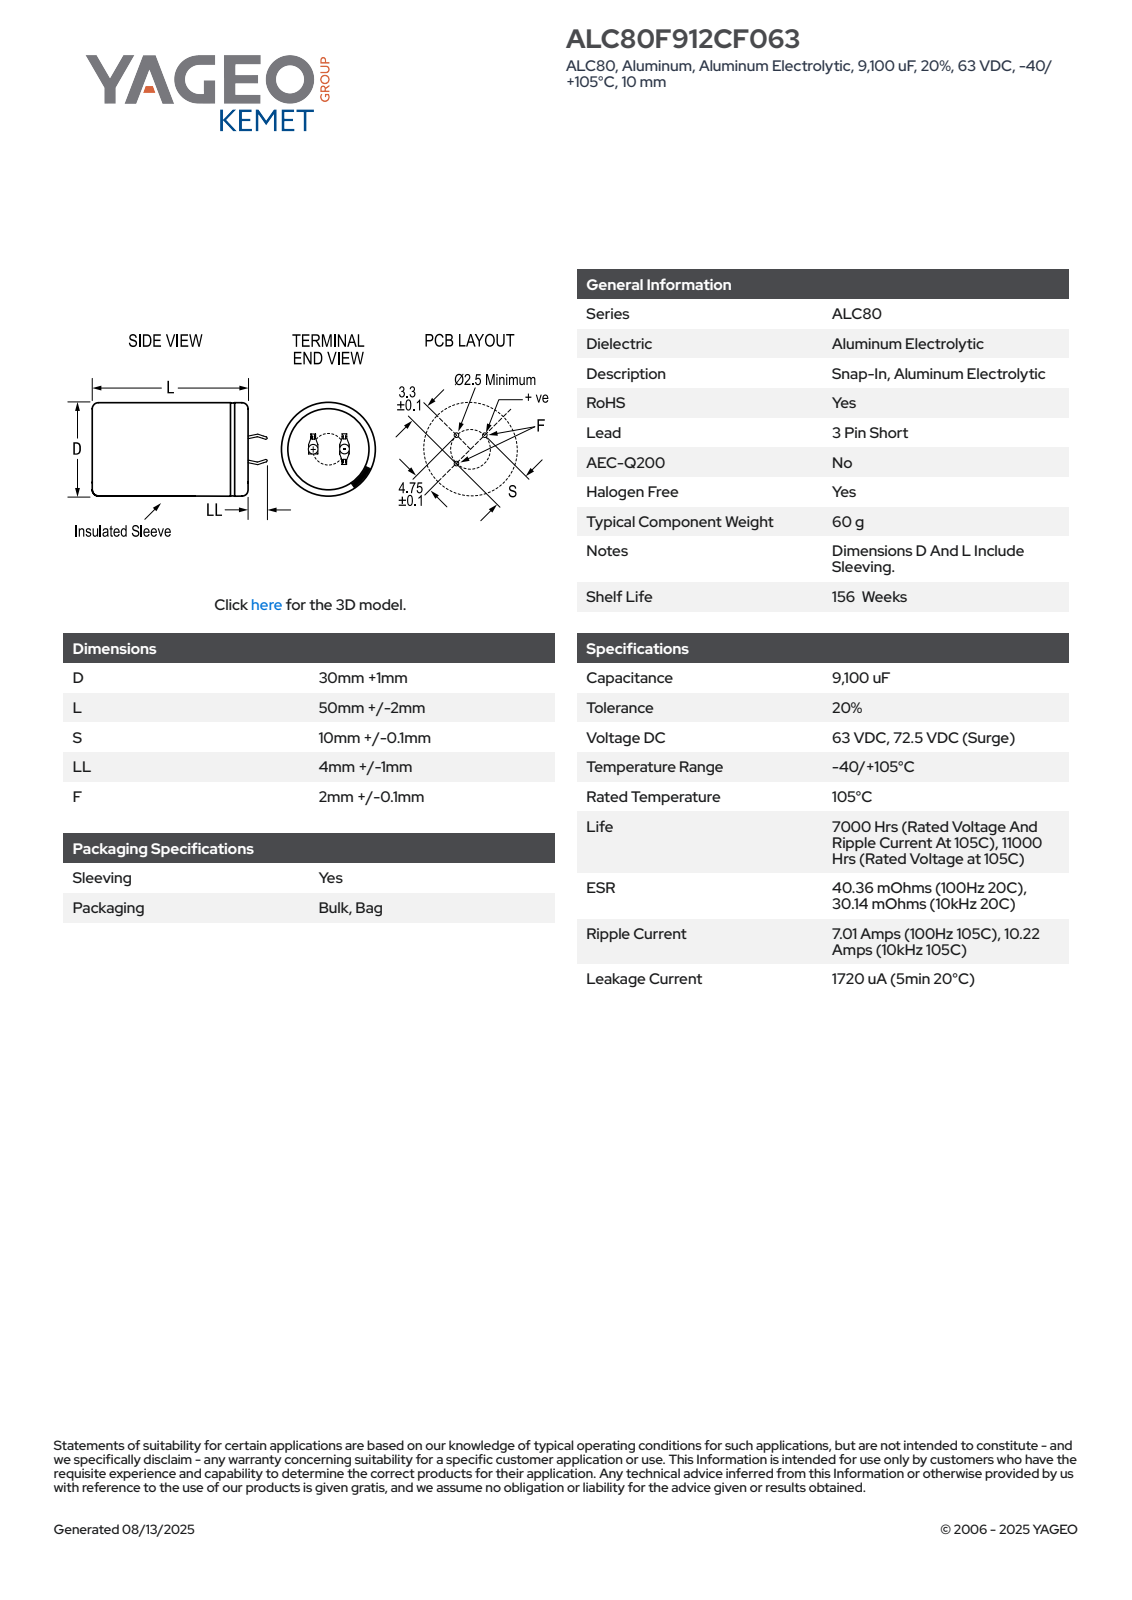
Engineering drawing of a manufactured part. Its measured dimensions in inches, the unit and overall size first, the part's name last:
Units: inches
Overall size (bounding box): 2.244 × 1.22 × 1.22
Round holes (diameter × count): ⌀1.08 ×1
Round bosses / shafts (diameter × count): ⌀1.22 ×1
Partial cylindrical surfaces — rounded edges, fillets, slot ends (radius × count): R0.61 ×1
Main face-to-face distances: 2.047, 2.067, 0.02, 0.024, 0.324, 0.023, 0.03, 0.053, 0.257, 0.083
Volume: 2.375 in³ · Surface area: 10.21 in²
Bodies: 1 solid, 115 faces (61 planar, 15 cylindrical, 39 other)
Part name (STEP PRODUCT): CARS_K3P_30X50_D31L52S10LL5F2.1
STEP written by: SolidWorks 2014 (AUTOMOTIVE_DESIGN)
